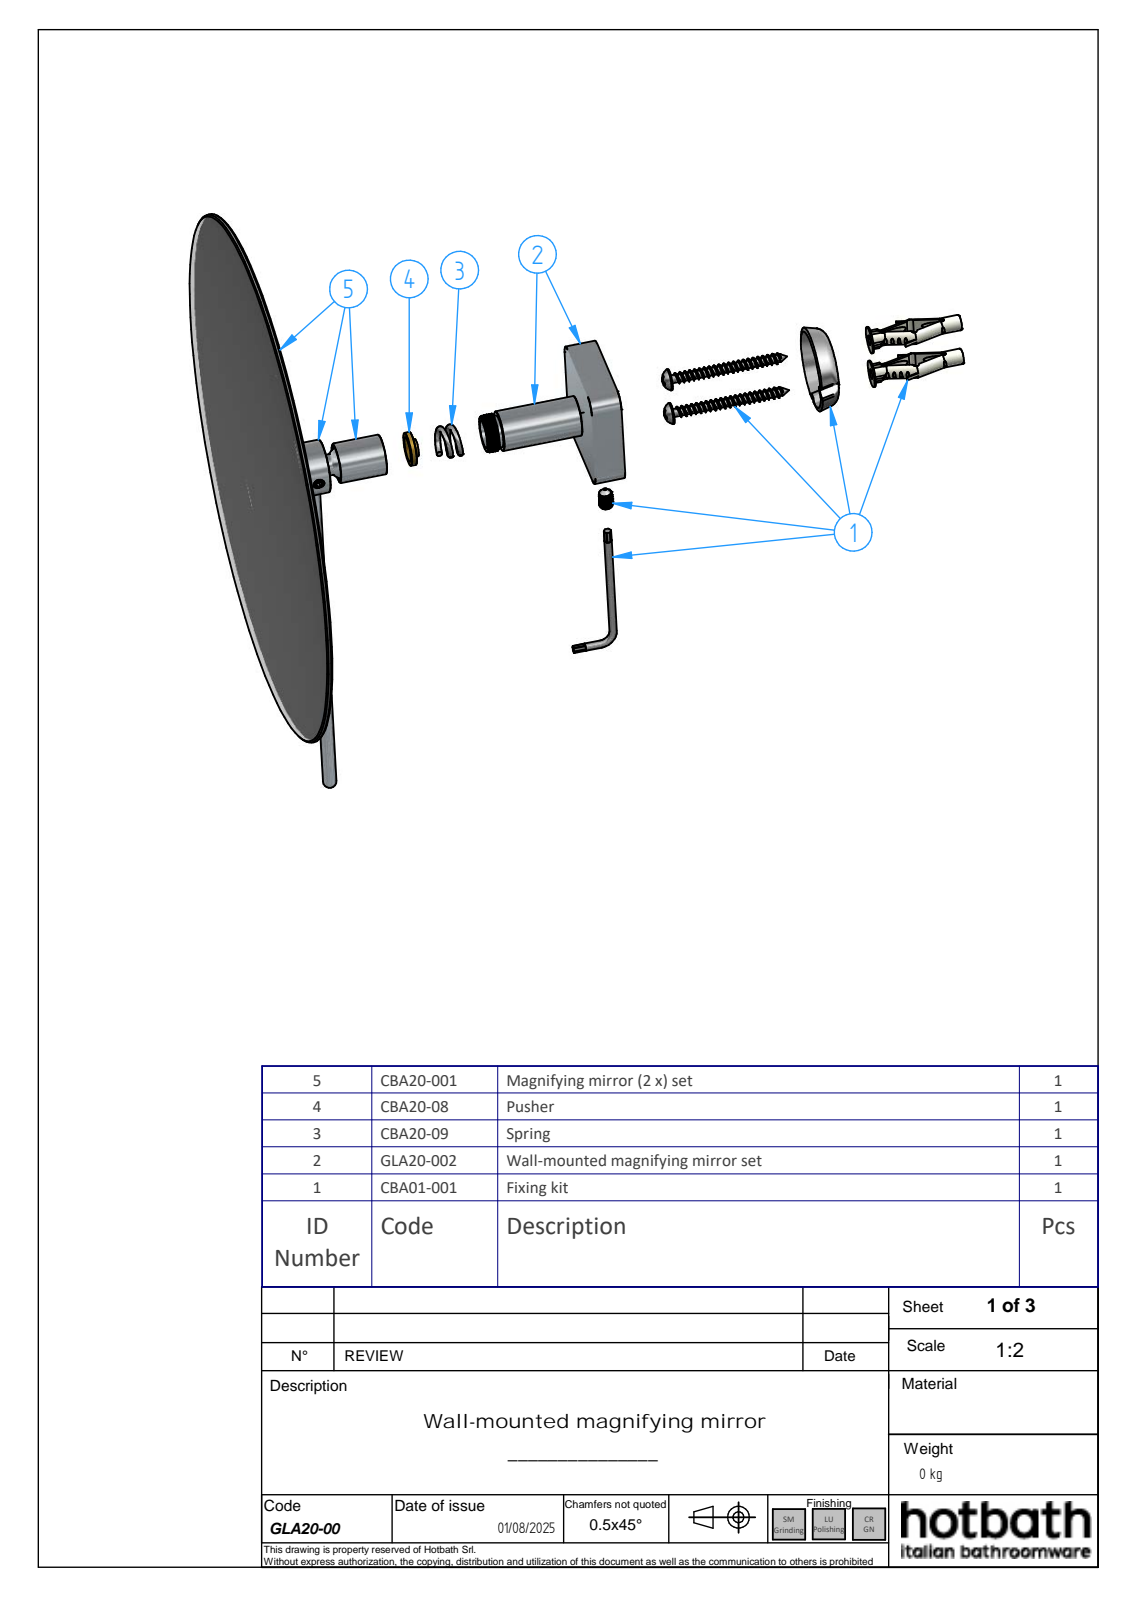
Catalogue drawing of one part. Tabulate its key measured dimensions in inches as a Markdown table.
| quantity | value |
| --- | --- |
| part name | GLA20-00 Rel1; CBA01-001_oa_0; CBA01-07; GLA20-002 Rel1_oa_1 (+8 more) |
| STEP written by | Solid Edge (AUTOMOTIVE_DESIGN) |
| units | inches |
| bodies | 10 solids, 206 faces (58 planar, 65 cylindrical, 83 other) |
| overall size | 9.88 × 7.869 × 3.543 |
| volume | 5.846 in³ |
| surface area | 160.6 in² |
| round holes (diameter × count) | 0.128 × 1, 0.157 × 1, 0.163 × 1, 0.167 × 1, 0.167 × 1, 0.194 × 1, 0.197 × 1, 0.236 × 1, 0.244 × 1, 0.351 × 1, 0.402 × 1, 0.413 × 1 |
| round bosses / shafts (diameter × count) | 0.197 × 2, 0.787 × 1, 0.591 × 1, 0.509 × 1, 0.472 × 1, 0.469 × 1, 0.433 × 1, 0.394 × 1 |
| partial cylindrical surfaces (radius × count) | 0.004 × 8, 0.197 × 4 |
| main face-to-face distances | 0.098, 2.514, 0.354, 0.039, 0.453, 2.415, 1.575, 2.868, 2.553, 2.455 |
| hole center spacings | 2.593 |
